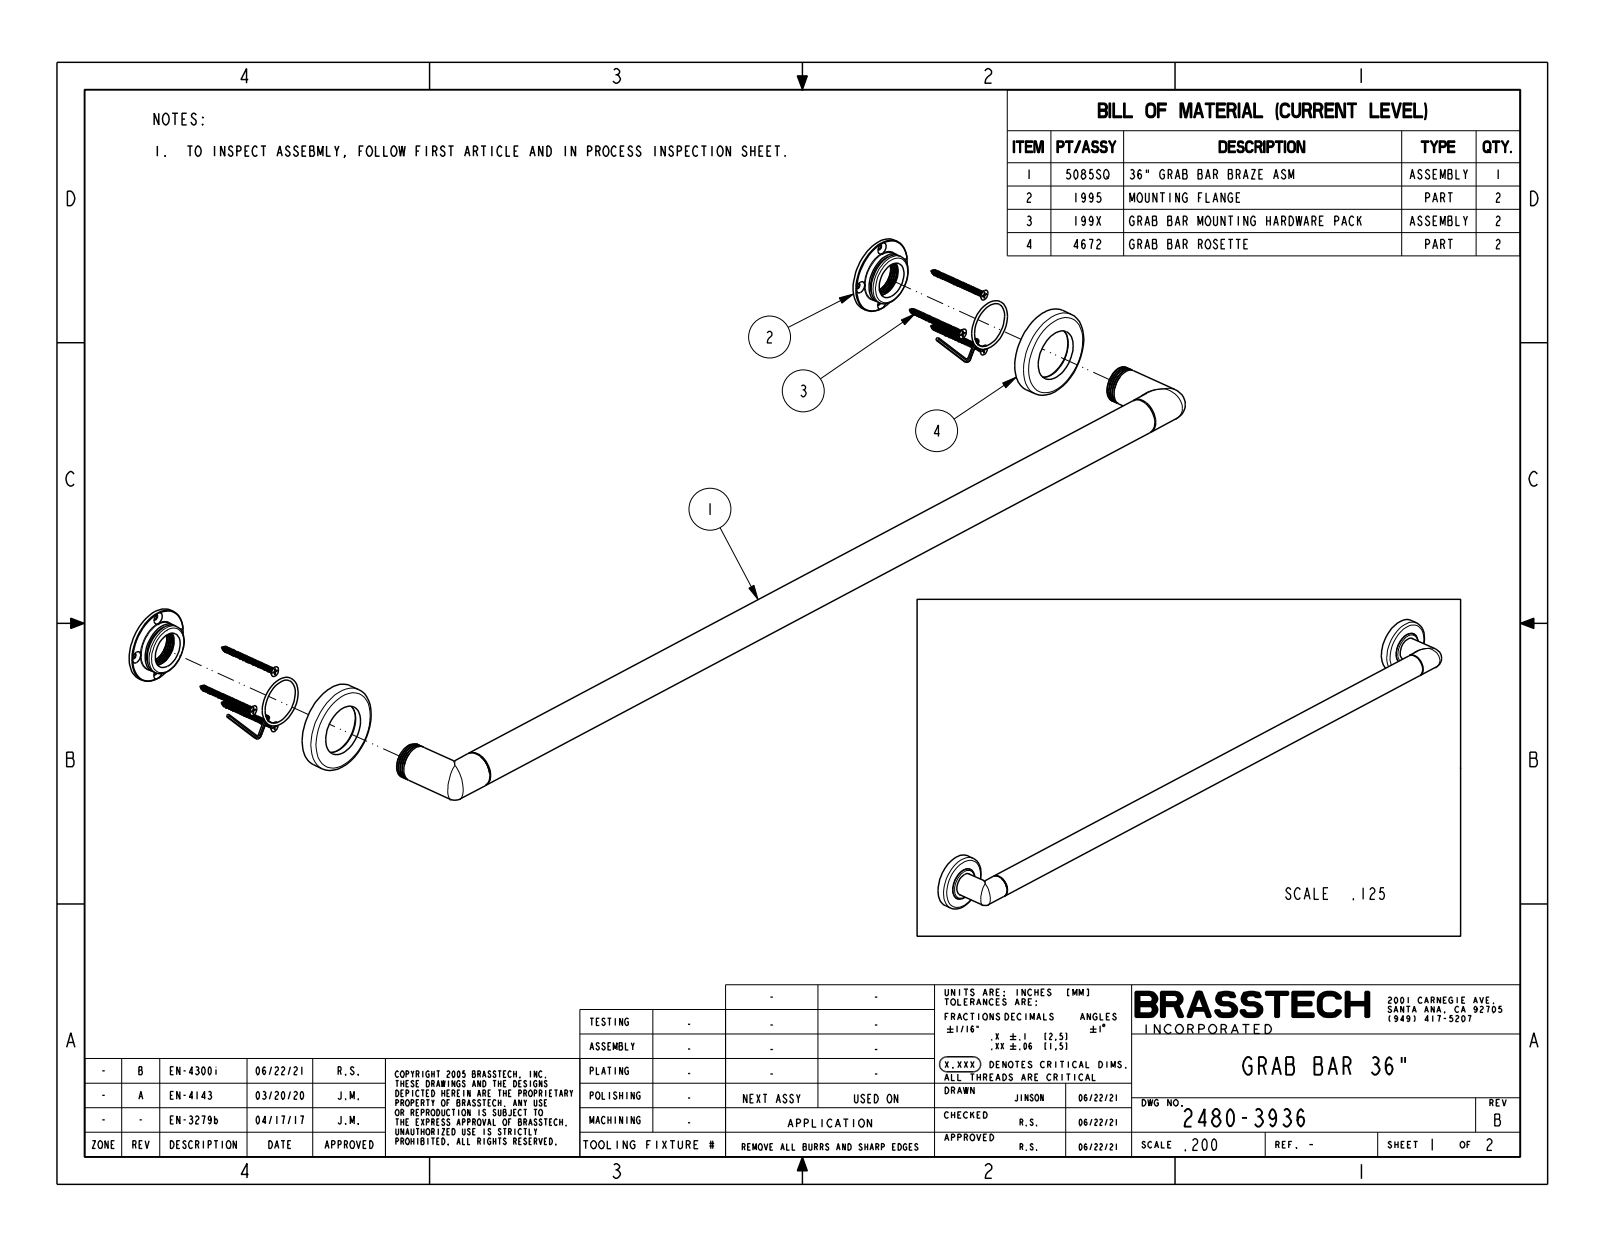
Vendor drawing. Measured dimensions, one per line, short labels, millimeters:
name: 2480-3936
written by: CREO PARAMETRIC BY PTC INC, 2018400 (CONFIG_CONTROL_DESIGN)
unit: mm
bodies: 1 solid, 48 faces (6 planar, 18 cylindrical, 24 other)
size: 990.6 × 76.2 × 70
volume: 911 800 mm³; area: 121 500 mm²
bosses: 3× ⌀31.8, 2× ⌀76.2, 2× ⌀44.5
face distances: 13.5, 15.2, 1.8
